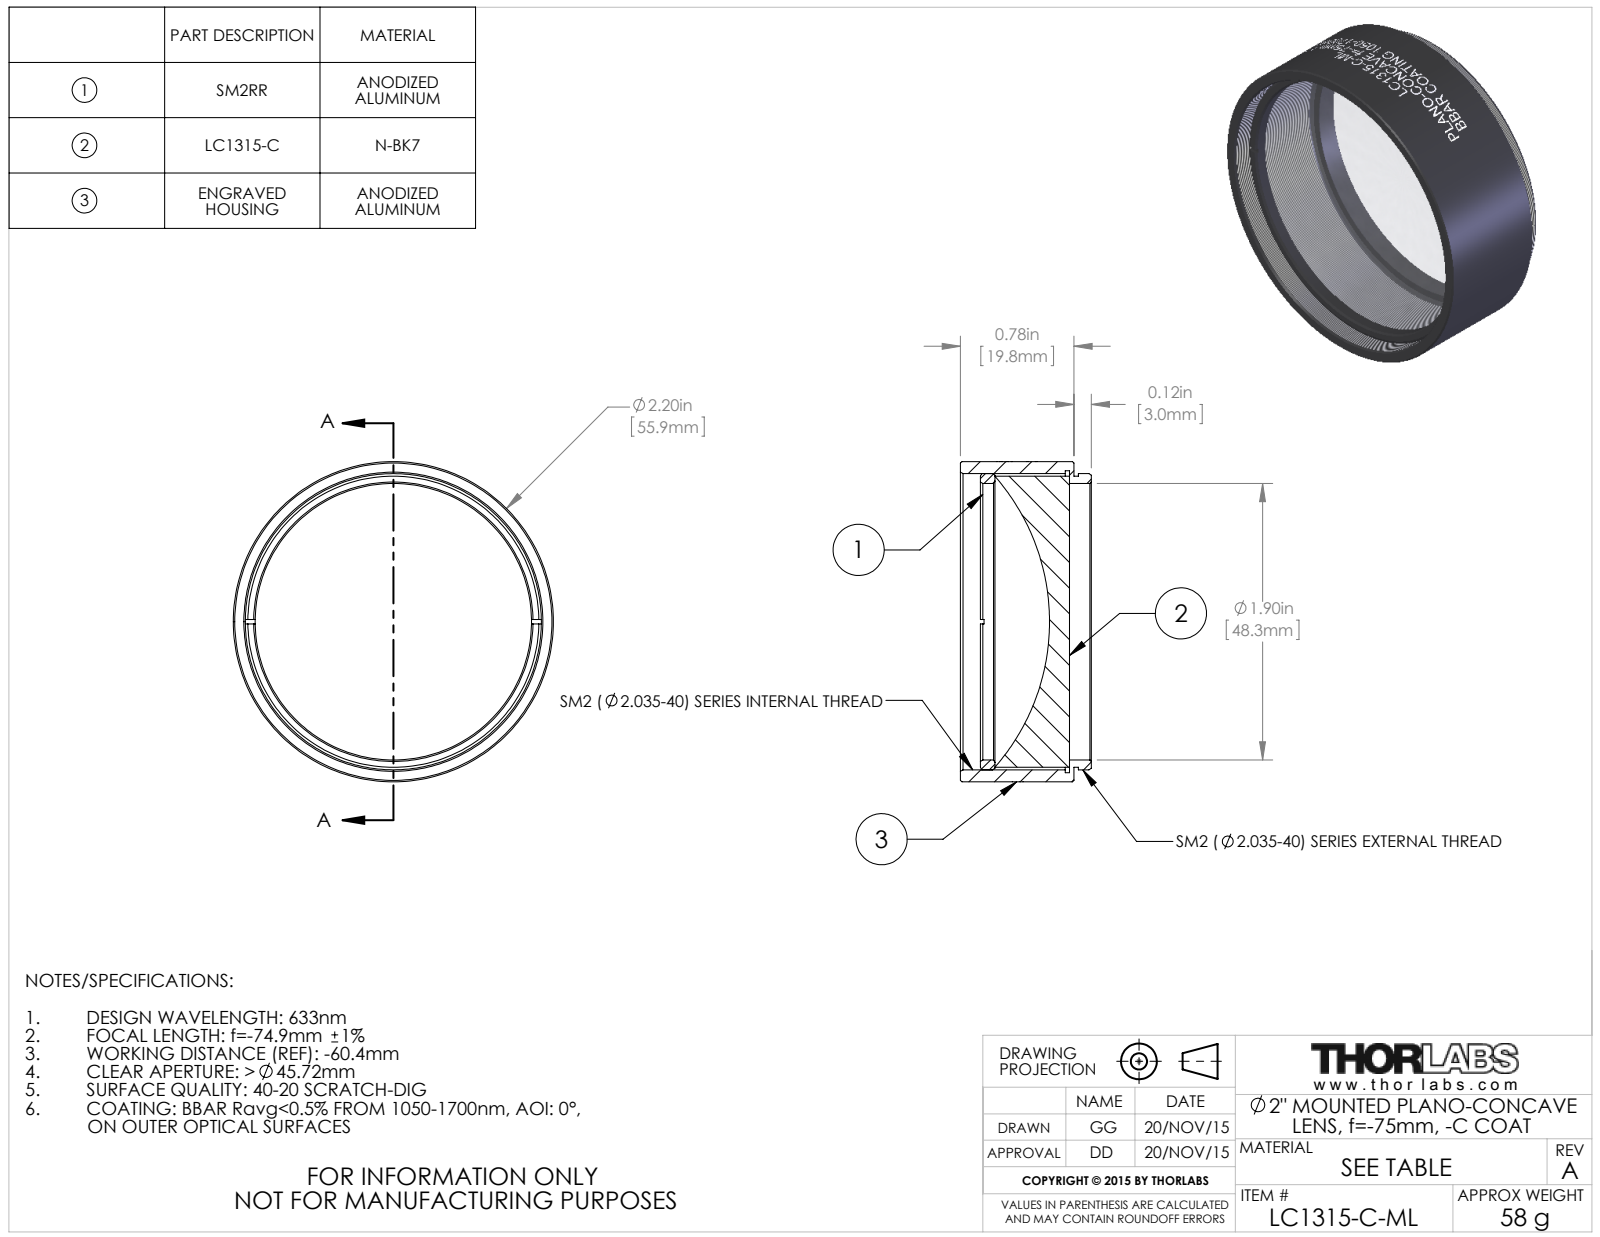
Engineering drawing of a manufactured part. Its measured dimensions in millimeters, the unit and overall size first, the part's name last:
Units: millimetres
Overall size (bounding box): 55.9 × 55.9 × 22.9
Round holes (diameter × count): ⌀48.3 ×1, ⌀52.7 ×1
Round bosses / shafts (diameter × count): ⌀55.9 ×1, ⌀51.7 ×1, ⌀50.8 ×1, ⌀50.8 ×1
Main face-to-face distances: 0.8, 19.8, 19.1, 3, 3.8, 22.9, 16.8, 13.8, 13, 6
Volume: 24 840 mm³ · Surface area: 16 710 mm²
Bodies: 3 solids, 144 faces (16 planar, 106 cylindrical, 22 other)
Part name (STEP PRODUCT): TTN045734-E0W
STEP written by: SolidWorks 2014 (CONFIG_CONTROL_DESIGN)
